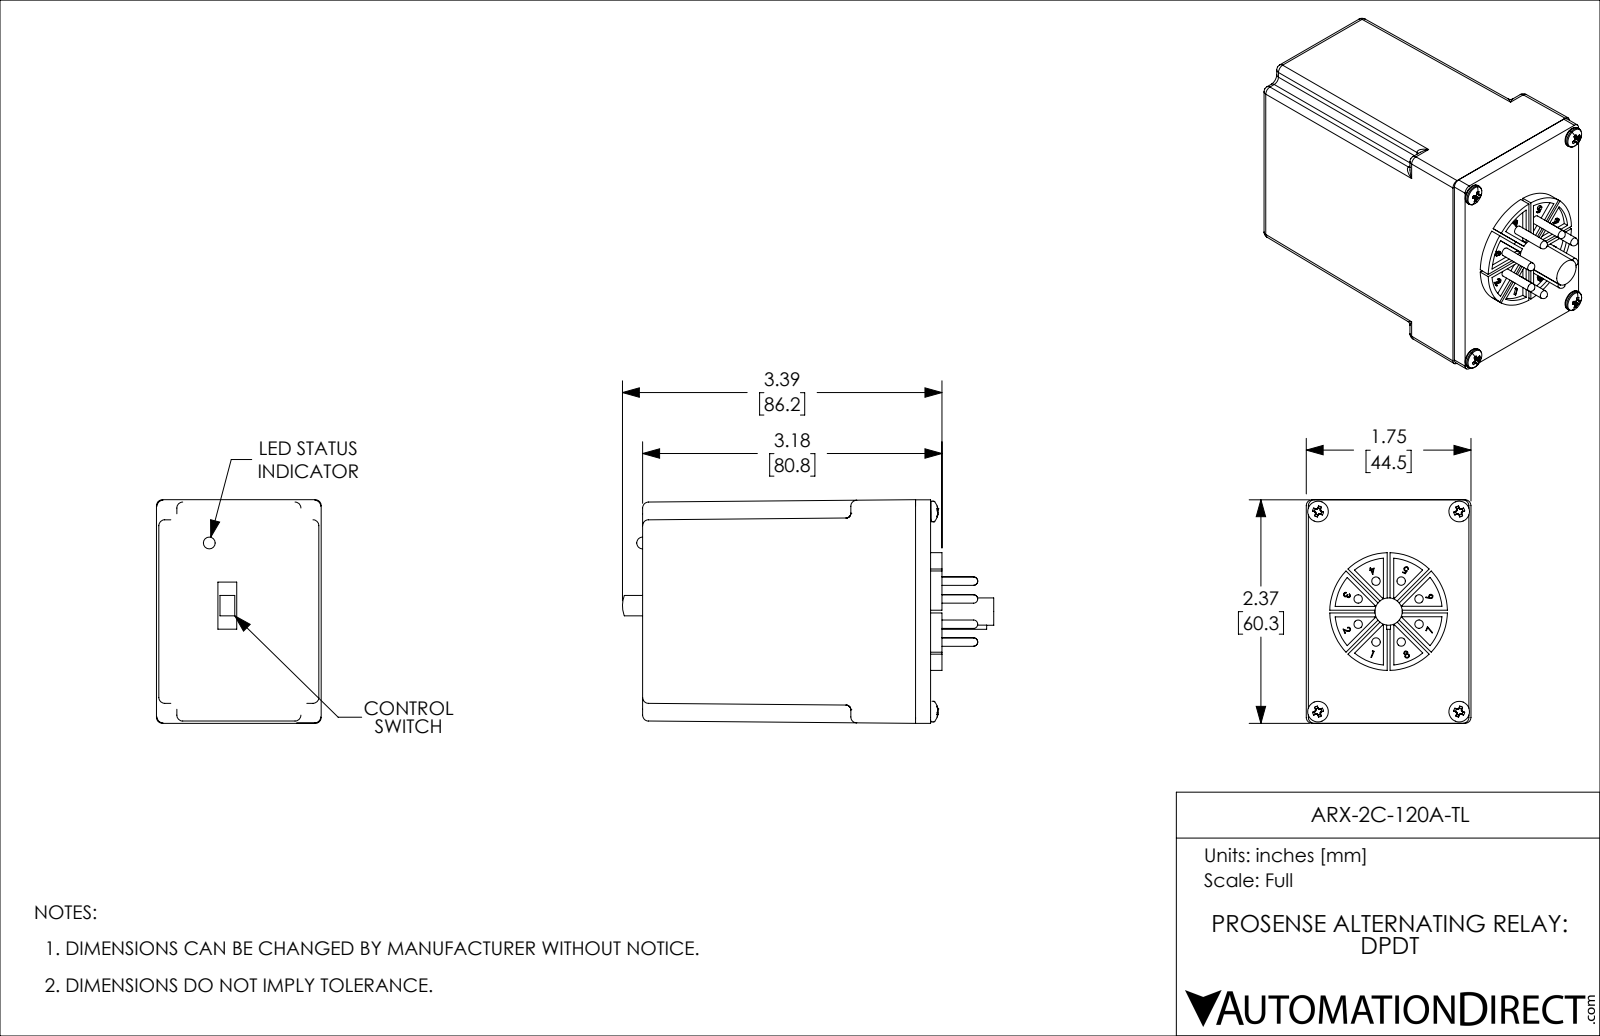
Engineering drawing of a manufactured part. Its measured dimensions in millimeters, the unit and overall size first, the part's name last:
Units: millimetres
Overall size (bounding box): 100.19 × 60.33 × 44.45
Main face-to-face distances: 73.66, 4.06, 77.72, 1.78, 5.84, 79.5, 4.77, 4.85, 1.27, 3.05
Volume: 200 510 mm³ · Surface area: 28 692 mm²
Bodies: 15 solids, 527 faces (145 planar, 0 cylindrical, 382 other)
Part name (STEP PRODUCT): ARX-2C-120A-TL
STEP written by: SolidWorks 2019 (AUTOMOTIVE_DESIGN)
